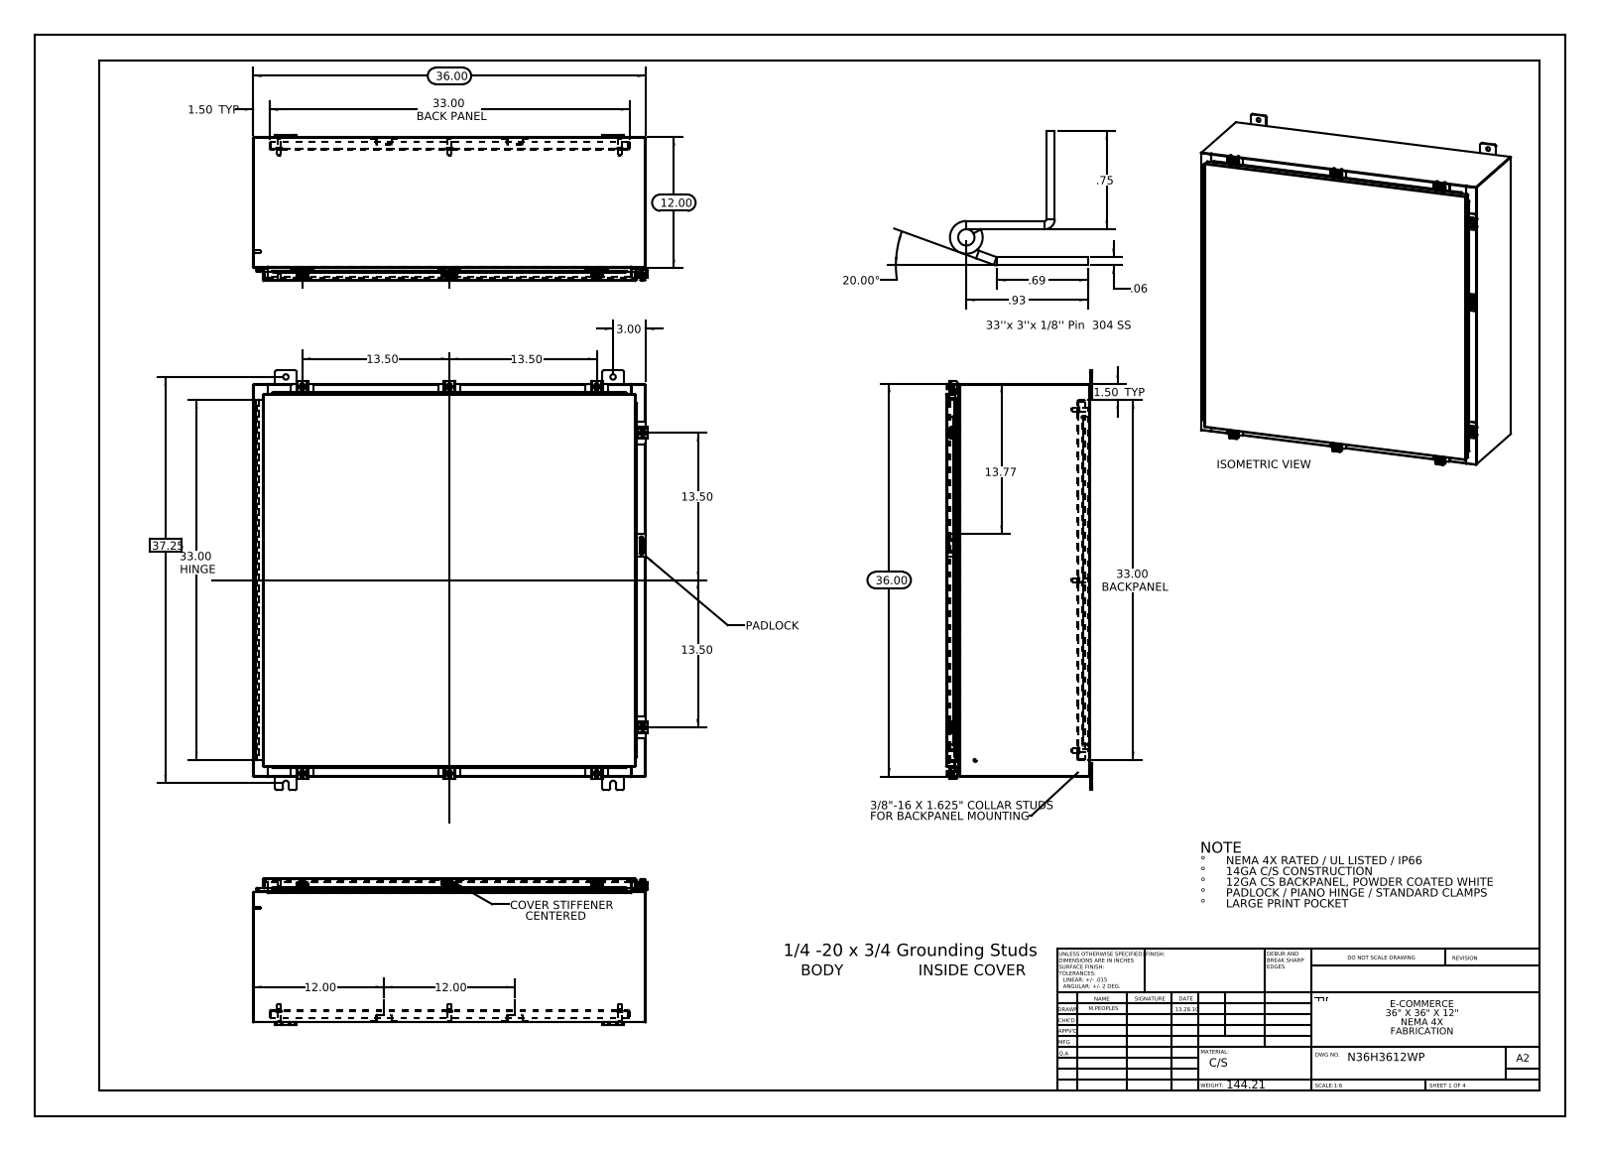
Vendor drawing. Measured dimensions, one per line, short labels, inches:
name: N36H3612SSWP Mounting Studs; N36H3612SSWP Clamp Top; N36H3612SSWP Backpanel; N36H3612SSWP 22101002 (+8 more)
written by: SolidWorks 2013 (CONFIG_CONTROL_DESIGN)
unit: in
bodies: 77 solids, 2710 faces (1382 planar, 1108 cylindrical, 220 other)
size: 38.5 × 36.211 × 13.389
volume: 505.7 in³; area: 12 670 in²
holes: 12× ⌀0.5, 9× ⌀0.213, 9× ⌀0.26, 6× ⌀0.25, 2× ⌀0.125
bosses: 10× ⌀0.25, 9× ⌀0.5, 9× ⌀0.399, 8× ⌀0.625, 8× ⌀0.375, 8× ⌀0.33, 6× ⌀0.157, 6× ⌀0.14
rounds: 42× R0.06, 39× R0.013, 33× R0.088, 24× R0.19, 18× R0.12, 18× R0.141, 13× R0.05, 12× R0.08
face distances: 0.075, 13.126, 35.925, 13.051, 13.201, 0.104, 12.126, 1, 1.075, 12.051
hole spacings: 13.5, 13.663, 15.625, 17.852, 23.629, 33.419, 34.095, 35.98
